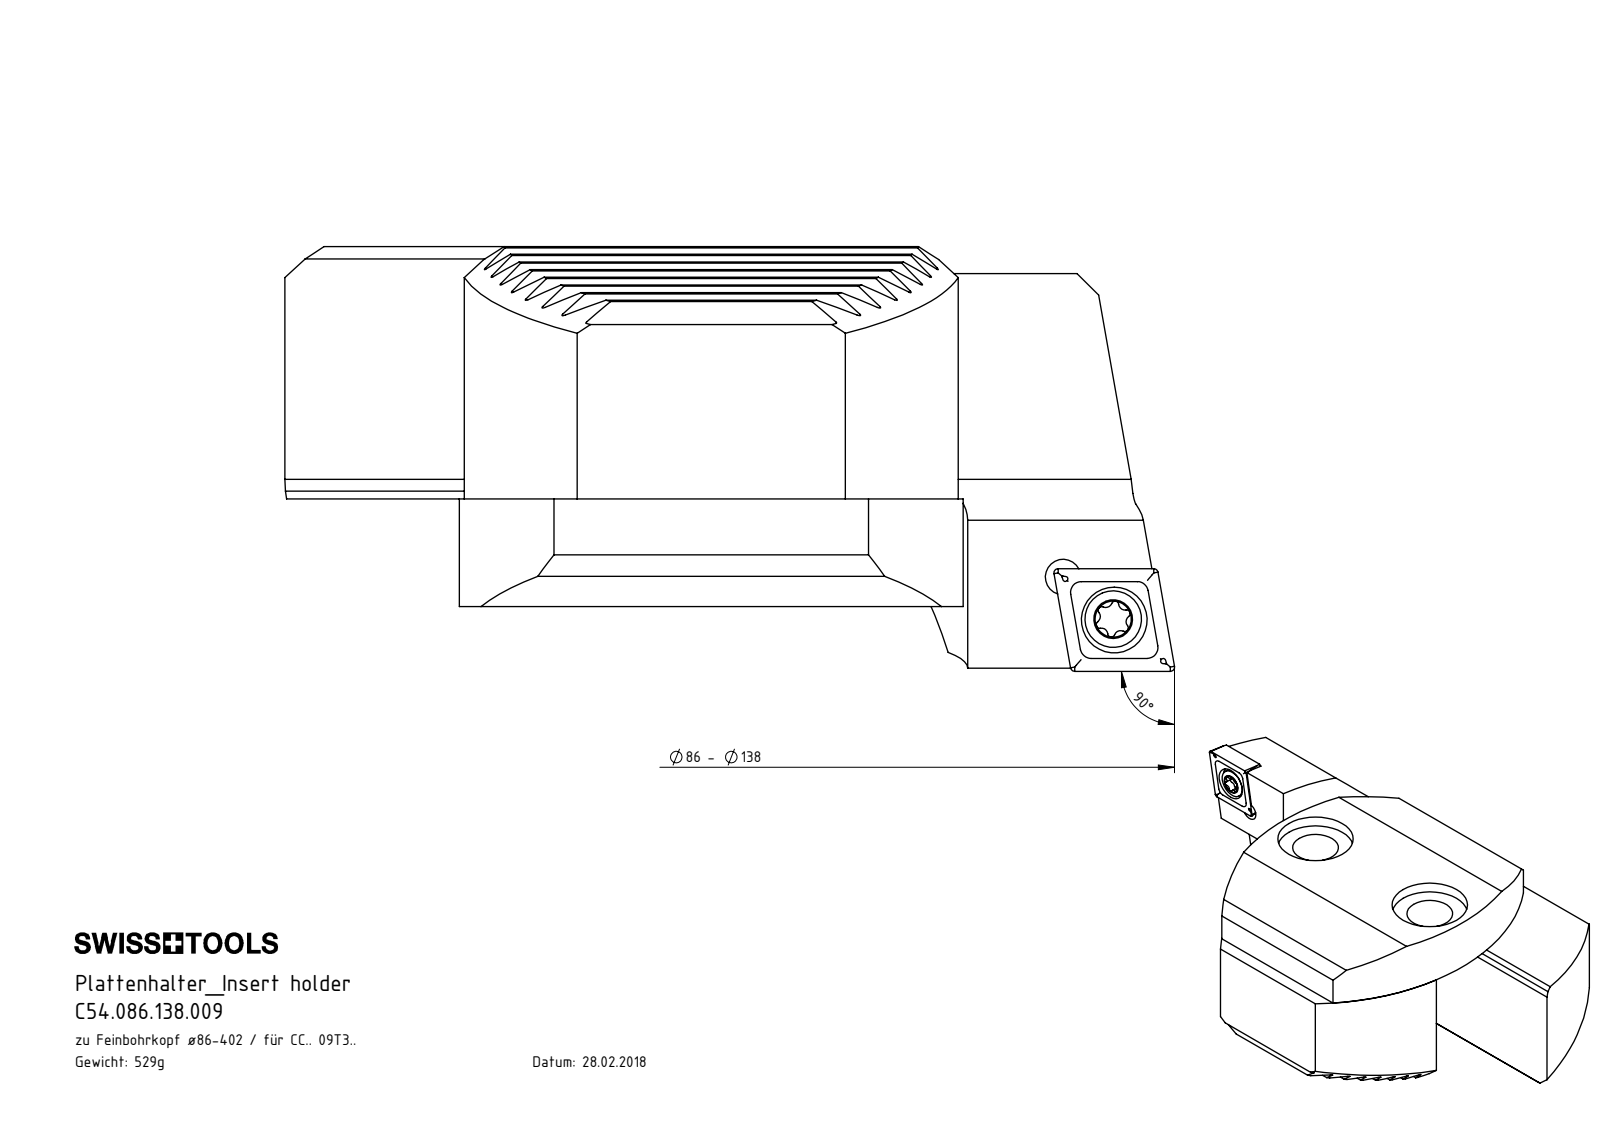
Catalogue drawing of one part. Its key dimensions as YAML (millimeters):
part_name: "C54.086.138.009; F00-WCB.086.003_A; F00-WCB.086.002_A; F00-WCB.086.001 (+3 more)"
step_written_by: "SolidWorks 2017 (CONFIG_CONTROL_DESIGN)"
units: millimeters
bodies: {solids: 5, faces: 442, planar: 264, cylindrical: 59, other: 119}
overall_size: [82.57, 55, 39.4]
volume: 67401
surface_area: 19323
round_holes:
  - {diameter: 3.3, count: 2}
  - {diameter: 8.5, count: 2}
  - {diameter: 14, count: 2}
  - {diameter: 4.4, count: 1}
  - {diameter: 6.1, count: 1}
round_bosses_or_shafts:
  - {diameter: 5.25, count: 1}
  - {diameter: 4, count: 1}
partial_cylinders:
  - {radius: 0.2, count: 16}
  - {radius: 40, count: 7}
  - {radius: 0.34, count: 6}
  - {radius: 0.59, count: 6}
  - {radius: 0.8, count: 1}
face_to_face_distances: [2.38, 21.3, 33.7, 4.76, 12.4, 10, 7.15, 9.53, 11.91, 7.14]
hole_center_spacings: [6.07, 6.2, 30]
